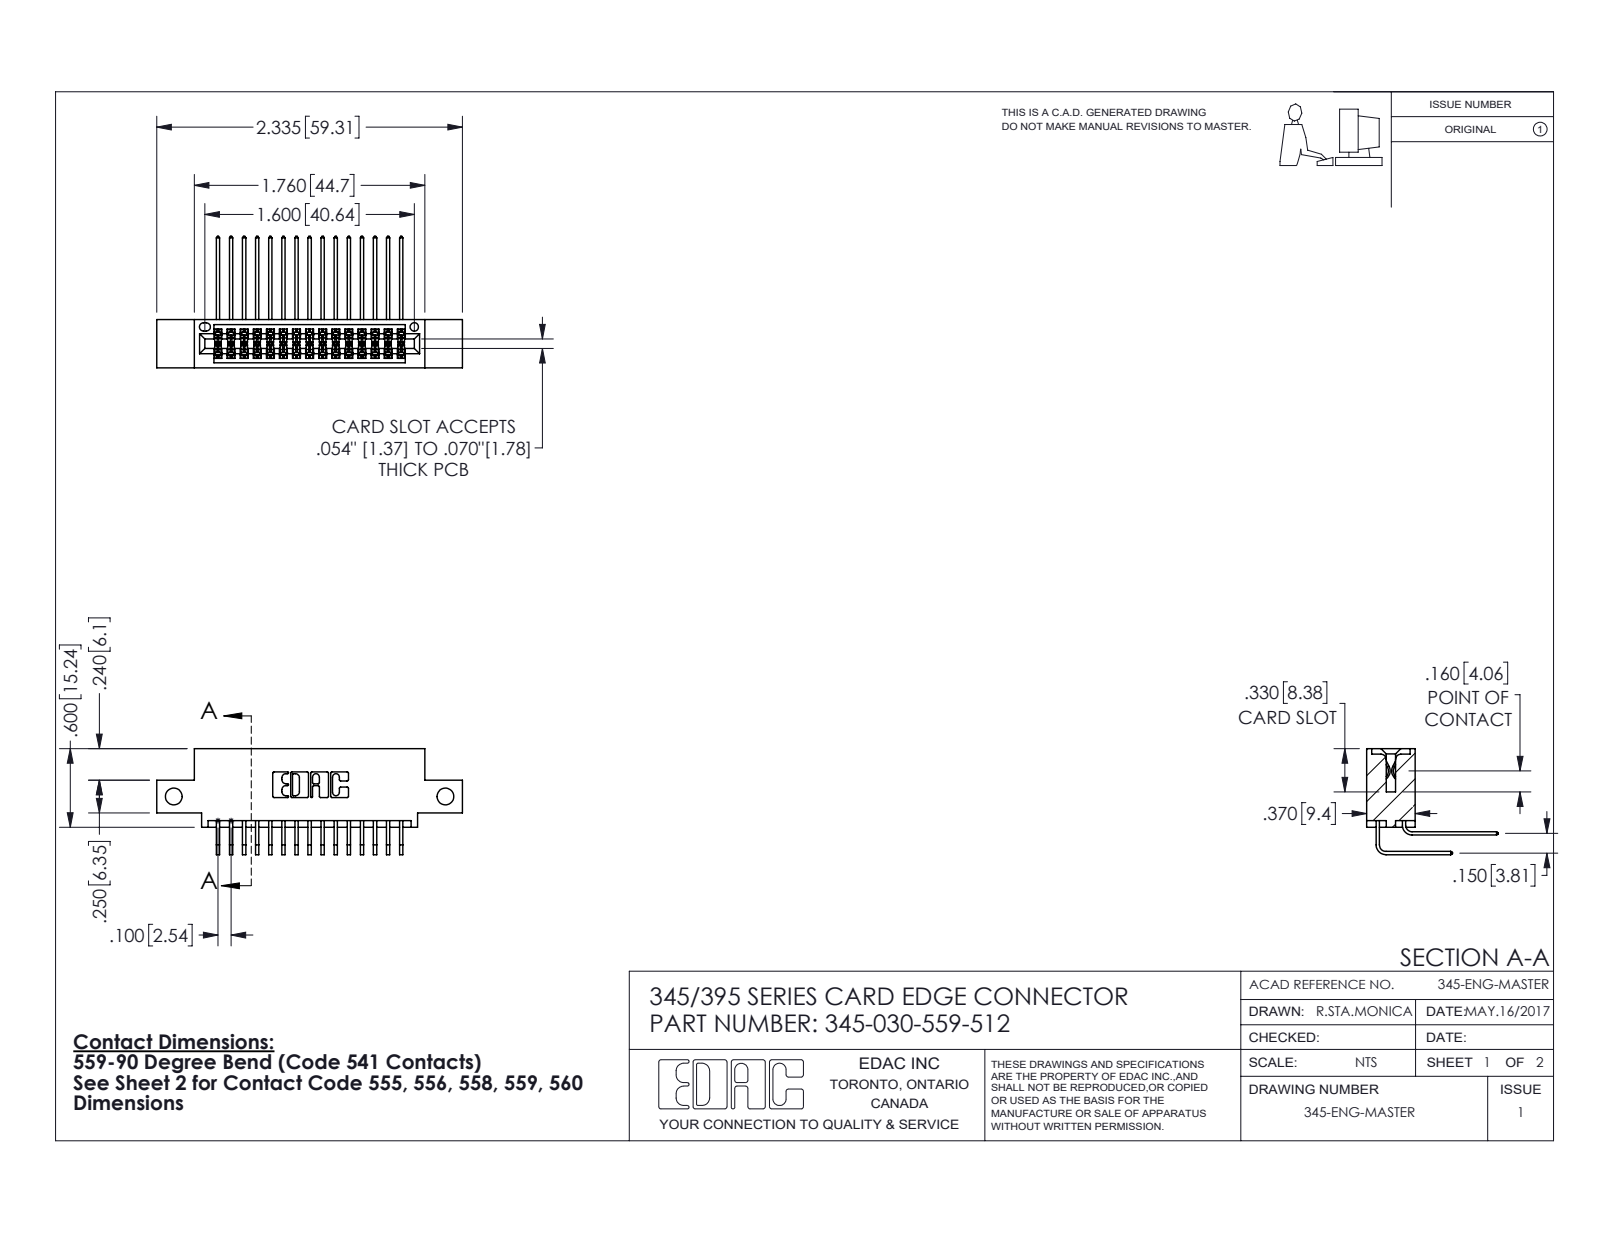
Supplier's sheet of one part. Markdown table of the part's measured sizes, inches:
| quantity | value |
| --- | --- |
| part name | 345-292-001_558 559 Tail - 1; 345-292-001_559 Tail - 2; 345-030-559-512; 345 Part_0.110 Offset - Side Mount |
| STEP written by | SolidWorks 2016 (CONFIG_CONTROL_DESIGN) |
| units | inches |
| bodies | 31 solids, 1690 faces (1134 planar, 556 cylindrical, 0 other) |
| overall size | 2.335 × 1.005 × 0.809 |
| volume | 0.337 in³ |
| surface area | 13.04 in² |
| round holes (diameter × count) | 0.128 × 2, 0.064 × 1 |
| partial cylindrical surfaces (radius × count) | 0.006 × 59, 0.01 × 22, 0.007 × 6, 0.031 × 6, 0.026 × 3, 0.014 × 2, 0.019 × 2, 0.022 × 2 |
| main face-to-face distances | 0.072, 0.298, 0.2, 0.37, 0.098, 0.272, 0.025, 0.225, 0.15, 0.175 |
| hole center spacings | 2.075 |
